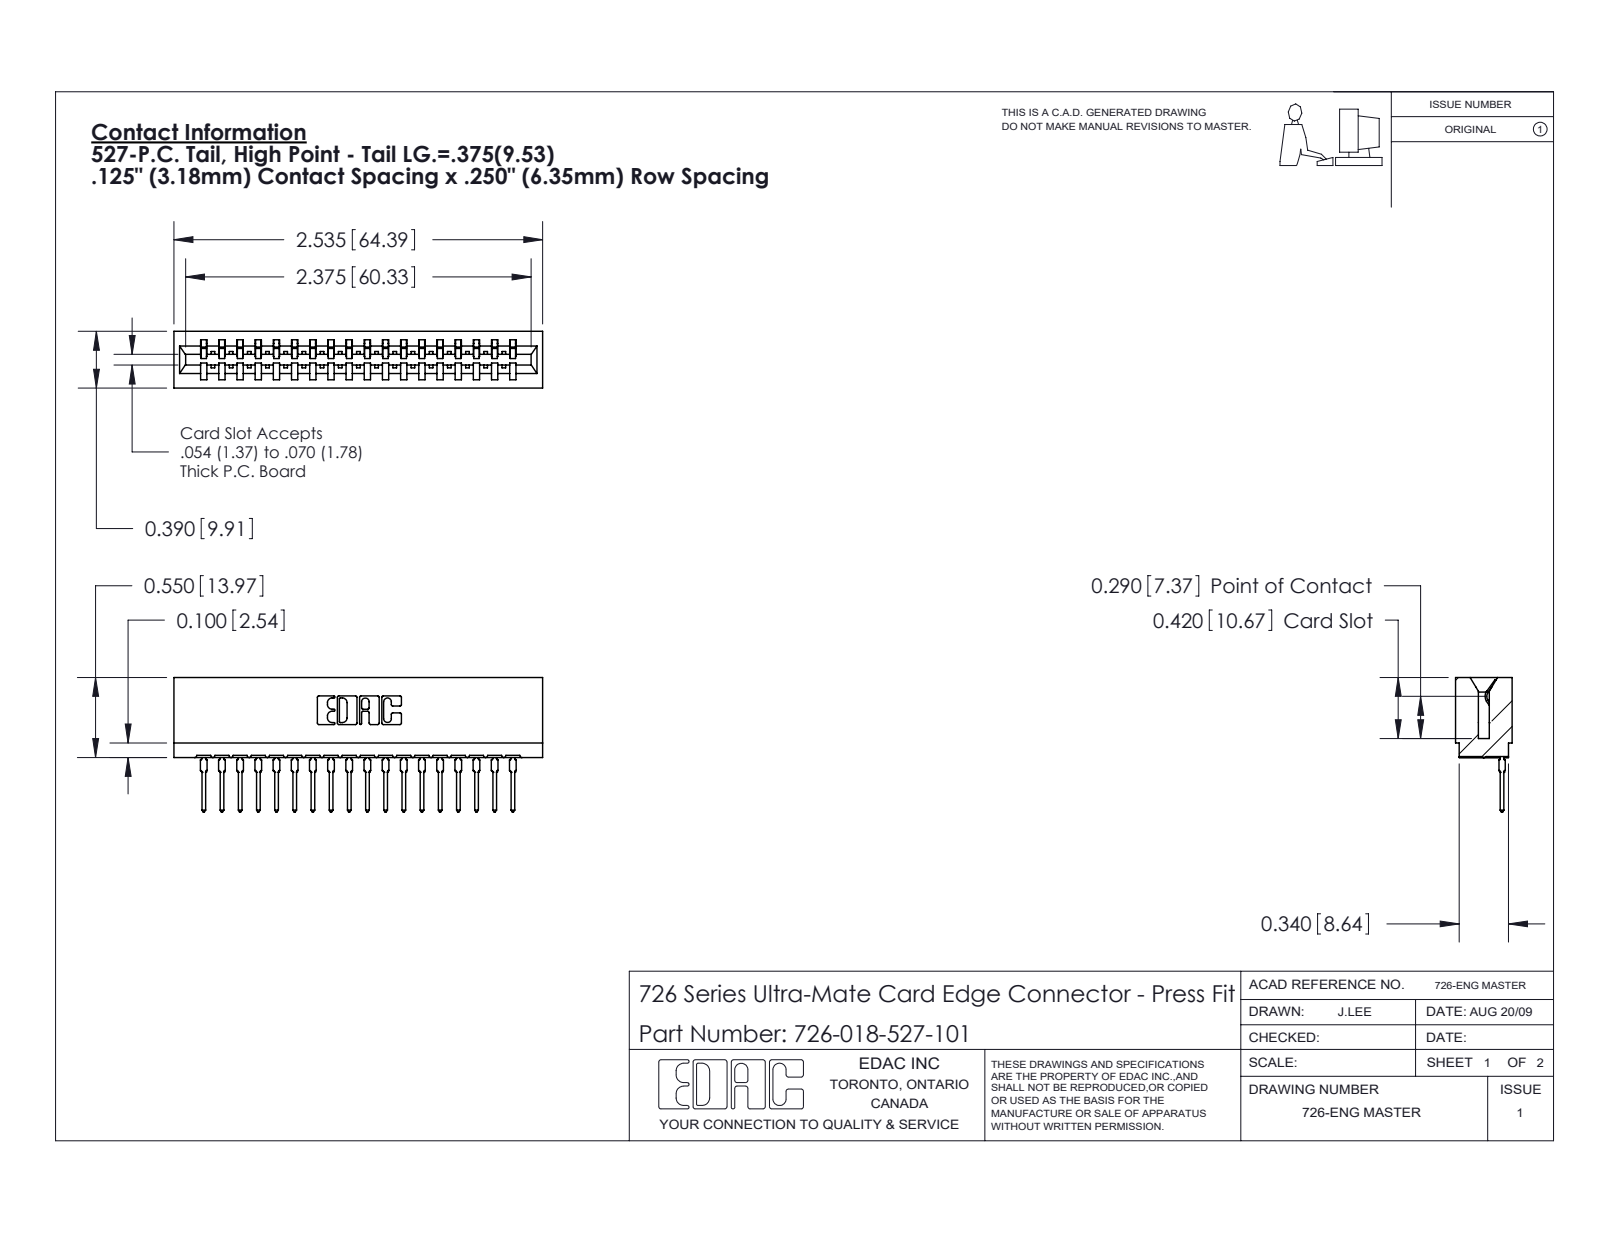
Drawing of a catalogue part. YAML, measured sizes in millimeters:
part_name: "726-018-527-101; 746-292-001_527; 726 Part_.515 Slot Depth - 01"
step_written_by: "SolidWorks 2020 (CONFIG_CONTROL_DESIGN)"
units: millimeters
bodies: {solids: 19, faces: 2041, planar: 1189, cylindrical: 384, other: 468}
overall_size: [64.4, 23.5, 9.9]
volume: 5900
surface_area: 8761
partial_cylinders:
  - {radius: 0.5, count: 36}
  - {radius: 0.3, count: 22}
  - {radius: 0.4, count: 19}
  - {radius: 0.2, count: 6}
  - {radius: 0.8, count: 6}
  - {radius: 0.1, count: 4}
  - {radius: 0.3, count: 4}
  - {radius: 0.7, count: 3}
face_to_face_distances: [1.4, 8.5, 9.9, 6.4, 0.6, 7.8, 19.1, 12.7, 2.1, 3.2]
